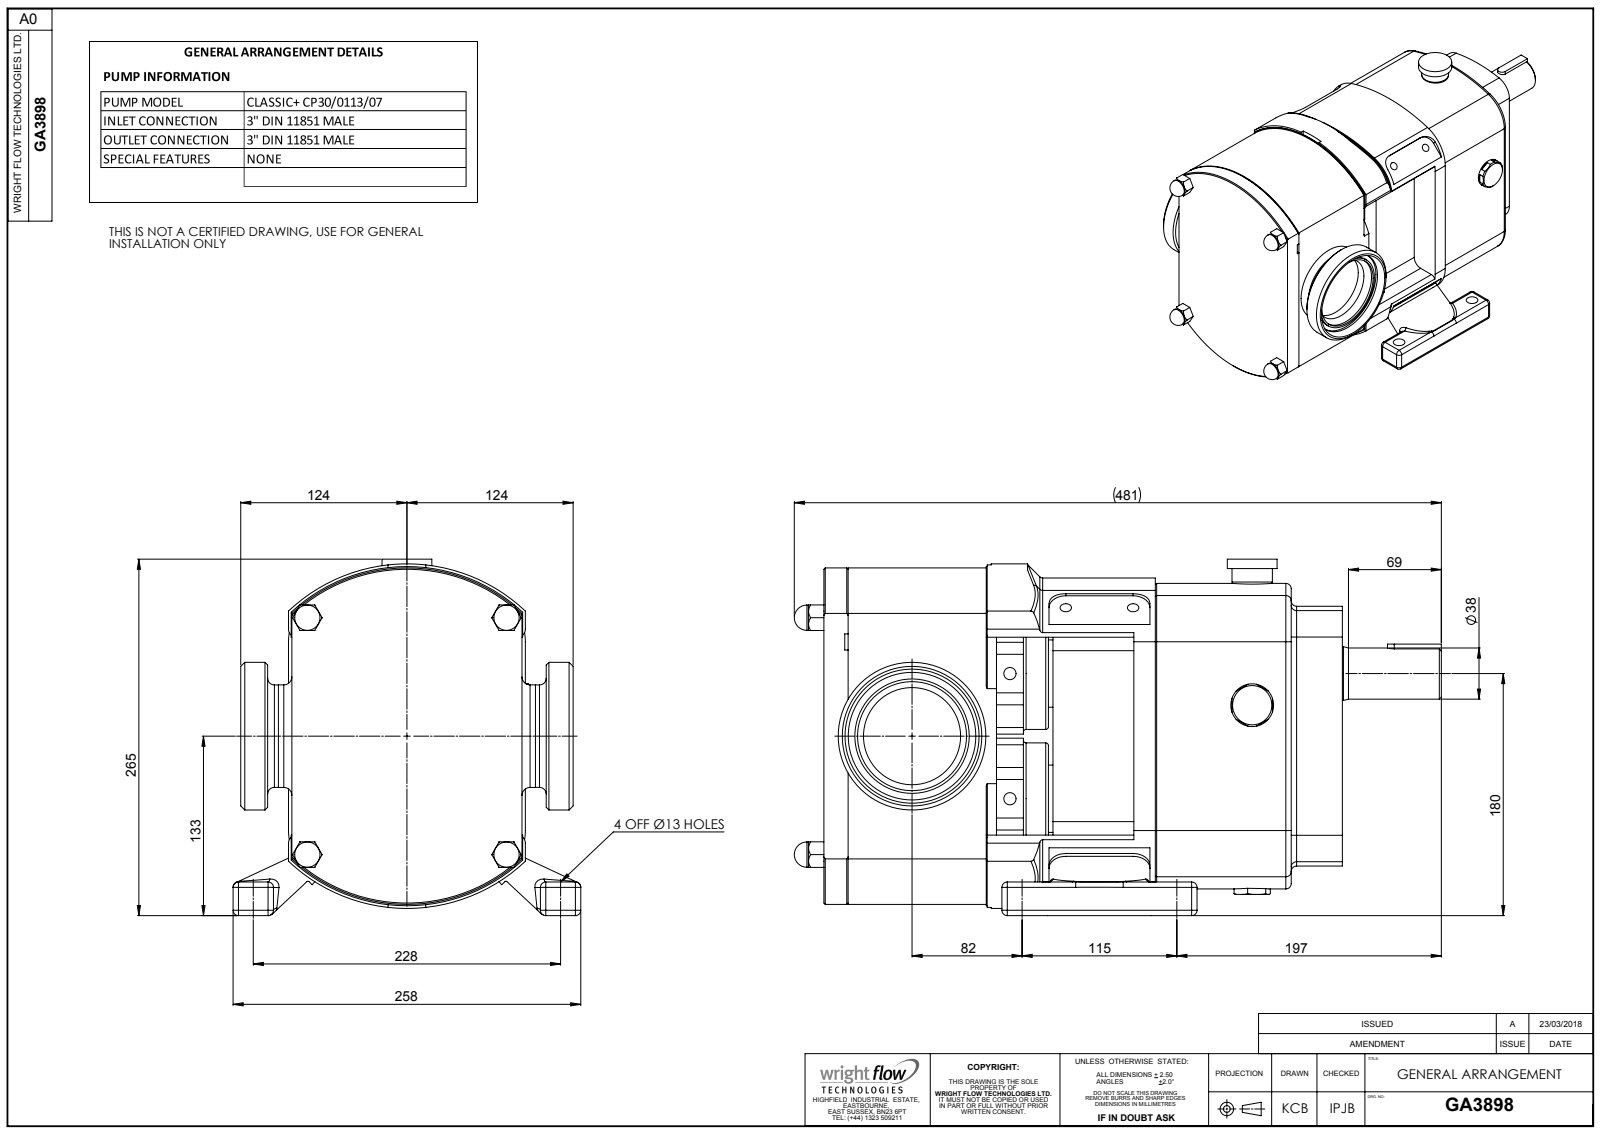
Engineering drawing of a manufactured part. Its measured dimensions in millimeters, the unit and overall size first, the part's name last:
Units: millimetres
Overall size (bounding box): 480.83 × 264.84 × 258.38
Round holes (diameter × count): ⌀8.5 ×4, ⌀10.11 ×4, ⌀13 ×4, ⌀9.09 ×2, ⌀35 ×1, ⌀72.2 ×1, ⌀81 ×1, ⌀94.8 ×1
Round bosses / shafts (diameter × count): ⌀18.8 ×4, ⌀83 ×2, ⌀50 ×2, ⌀109.7 ×1, ⌀85 ×1, ⌀76.2 ×1, ⌀76.1 ×1, ⌀40.01 ×1
Partial cylindrical surfaces — rounded edges, fillets, slot ends (radius × count): R4 ×44, R1 ×16, R10 ×12, R6 ×10, R12.5 ×4, R12.57 ×4, R12.6 ×4, R20 ×4
Main face-to-face distances: 1.5, 169.5, 139, 38, 170.23, 215.05, 385.28, 171, 30.5, 140.5
Hole centre spacings: 63.64, 50.05, 86.34, 90, 115, 228.39, 255.71, 93
Volume: 13 010 000 mm³ · Surface area: 579 167 mm²
Bodies: 3 solids, 737 faces (269 planar, 249 cylindrical, 219 other)
Part name (STEP PRODUCT): Copy of Z94-5031-55 - 3 INCH DIN11851^GA3898; GA3898; Copy of CP30-0113-07 H T^GA3898
STEP written by: SolidWorks 2023 (AUTOMOTIVE_DESIGN)
